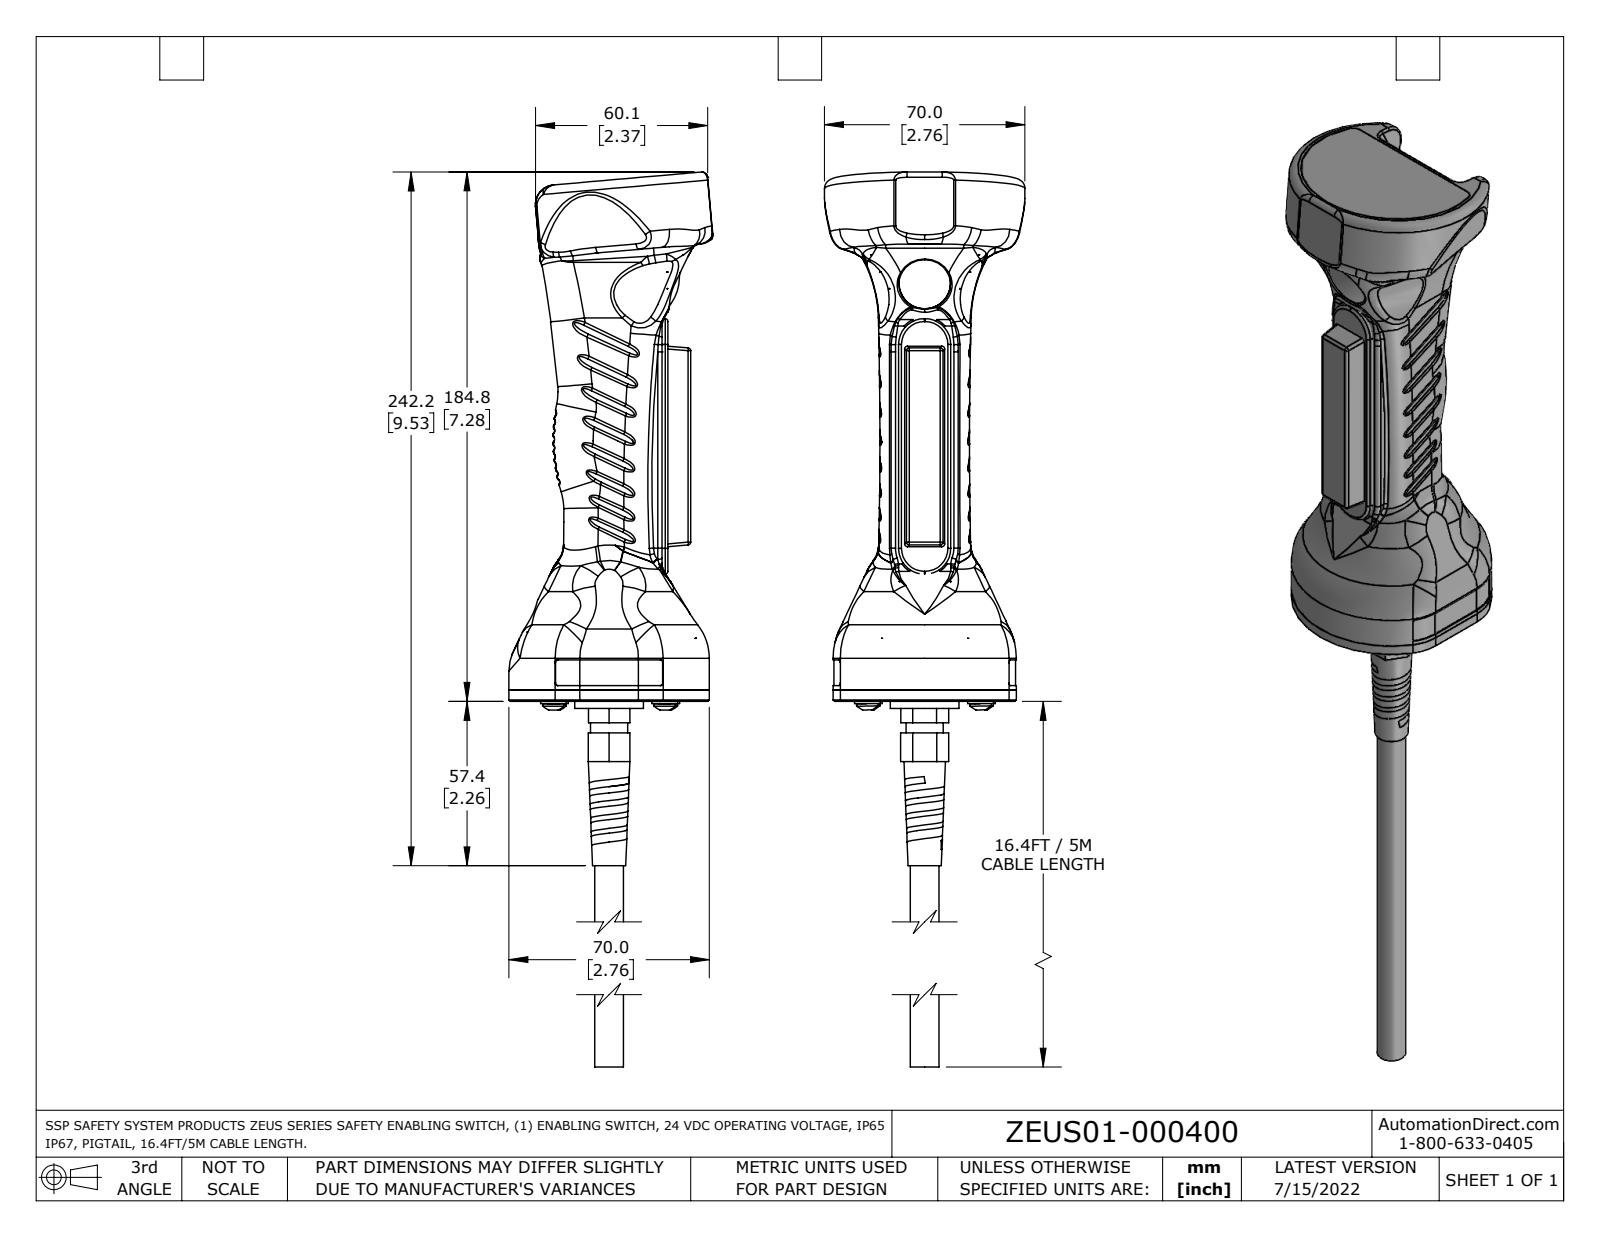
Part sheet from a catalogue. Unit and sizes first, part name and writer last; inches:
Units: inches
Overall size (bounding box): 14.926 × 2.803 × 2.756
Round holes (diameter × count): ⌀0.132 ×4, ⌀0.169 ×4, ⌀0.177 ×4, ⌀0.197 ×4, ⌀0.098 ×2, ⌀0.11 ×2, ⌀0.165 ×2, ⌀0.331 ×2, ⌀0.394 ×1, ⌀0.417 ×1, ⌀0.551 ×1, ⌀0.709 ×1
Round bosses / shafts (diameter × count): ⌀0.354 ×4, ⌀0.295 ×4, ⌀0.157 ×4, ⌀0.039 ×4, ⌀0.236 ×2, ⌀0.945 ×1, ⌀0.827 ×1, ⌀0.776 ×1
Partial cylindrical surfaces — rounded edges, fillets, slot ends (radius × count): R0.005 ×96, R0.039 ×51, R0.028 ×48, R0.079 ×21, R0.118 ×10, R0.031 ×7, R0.012 ×5, R0.618 ×4
Main face-to-face distances: 0.157, 0.079, 0.014, 0.065, 0.02, 0.059, 0.098, 0.177, 0.571, 0.472
Hole centre spacings: 0.866, 1.08, 1.181, 1.531, 0.63, 1.558, 0.404, 0.404
Volume: 23.73 in³ · Surface area: 126 in²
Bodies: 16 solids, 1140 faces (321 planar, 397 cylindrical, 422 other)
Part name (STEP PRODUCT): ZEUS01-000400
STEP written by: SolidWorks 2021 (AUTOMOTIVE_DESIGN)
